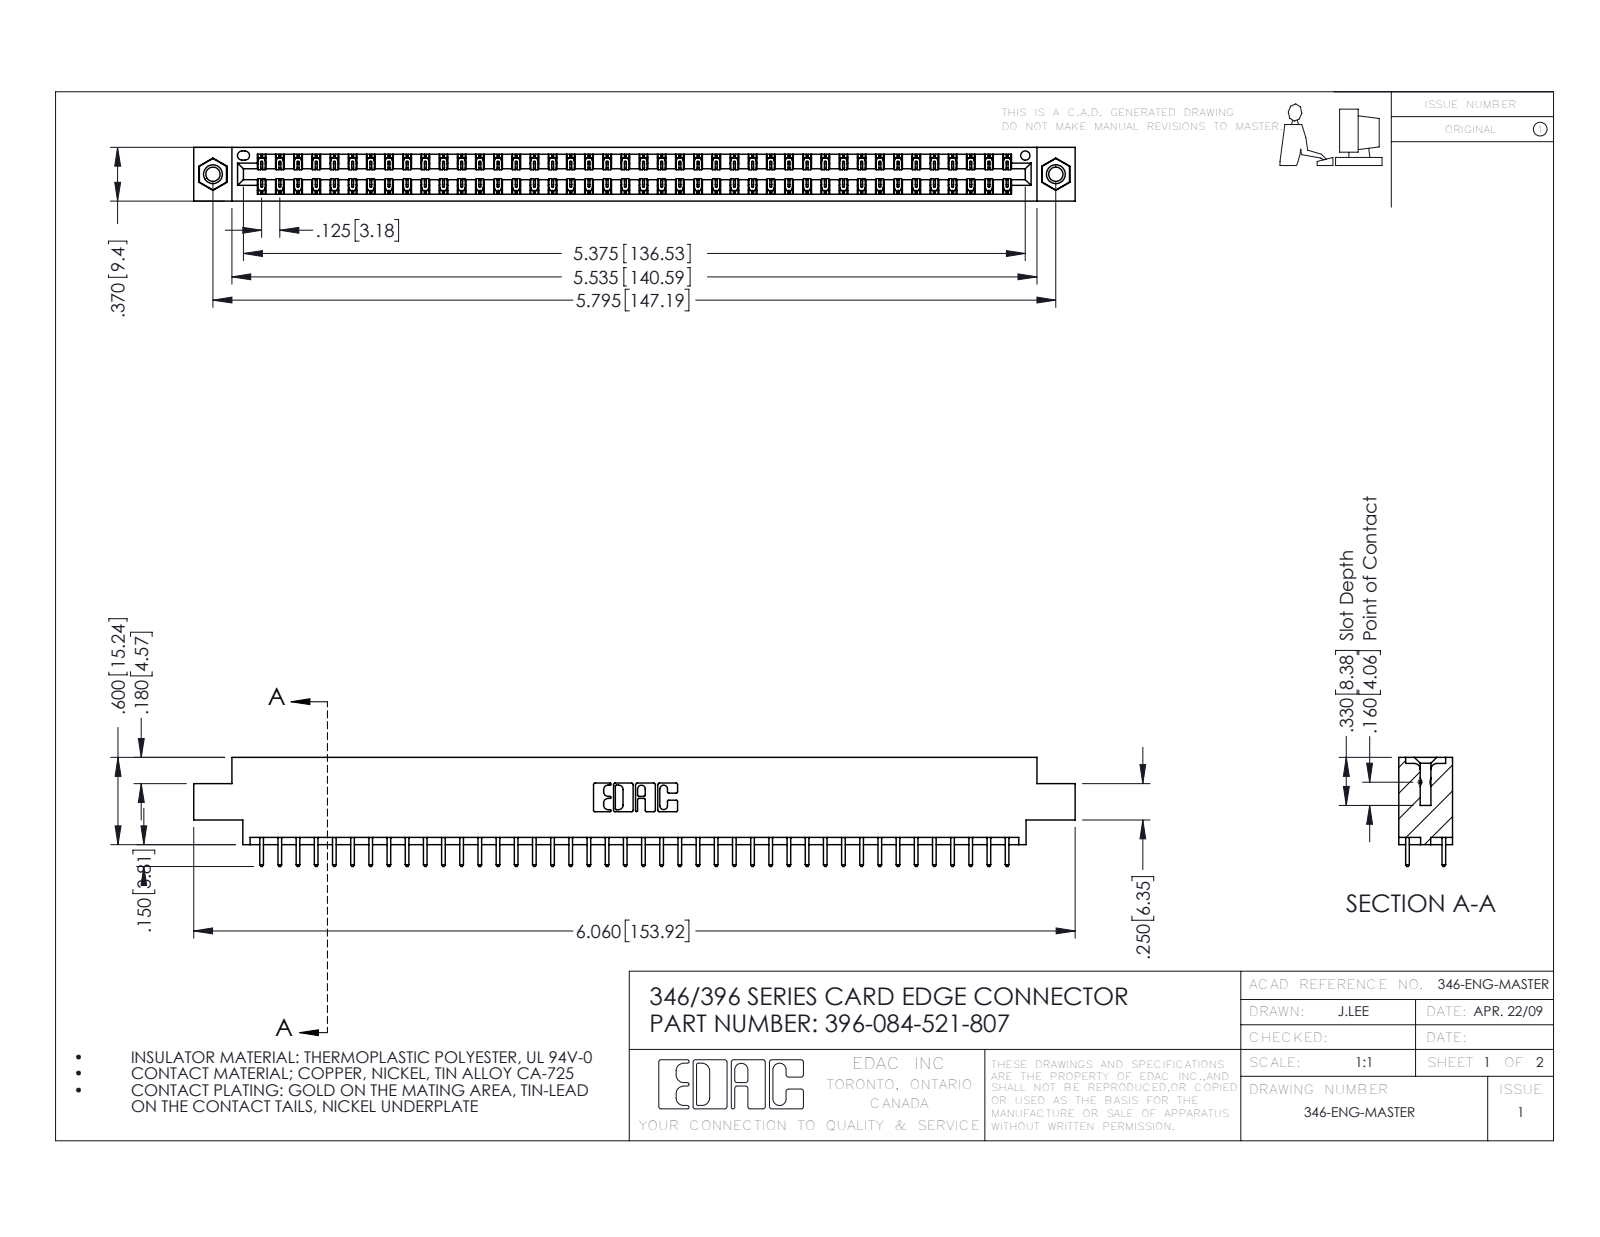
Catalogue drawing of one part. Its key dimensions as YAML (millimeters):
part_name: "345-250-001_345-250-005-103; 396-084-521-807; 346 Part_0.170 Offset - 0.156 Dia-TI; 345-292-001_345-293-121"
step_written_by: "SolidWorks 2016 (CONFIG_CONTROL_DESIGN)"
units: millimeters
bodies: {solids: 87, faces: 4554, planar: 3052, cylindrical: 1486, other: 16}
overall_size: [153.9, 19.1, 9.4]
volume: 14800
surface_area: 20340
round_holes:
  - {diameter: 2.5, count: 2}
  - {diameter: 3.2, count: 2}
  - {diameter: 4, count: 2}
  - {diameter: 1.6, count: 1}
round_bosses_or_shafts:
  - {diameter: 3.9, count: 2}
partial_cylinders:
  - {radius: 0.2, count: 126}
  - {radius: 0.3, count: 84}
  - {radius: 0.3, count: 22}
  - {radius: 0.2, count: 6}
  - {radius: 0.8, count: 6}
  - {radius: 0.7, count: 3}
  - {radius: 0.4, count: 2}
  - {radius: 0.6, count: 2}
face_to_face_distances: [1.2, 8.2, 9.4, 6.4, 1.8, 7.6, 0.6, 7, 5.6, 3.8]
hole_center_spacings: [6.2, 141.9, 147.2]
